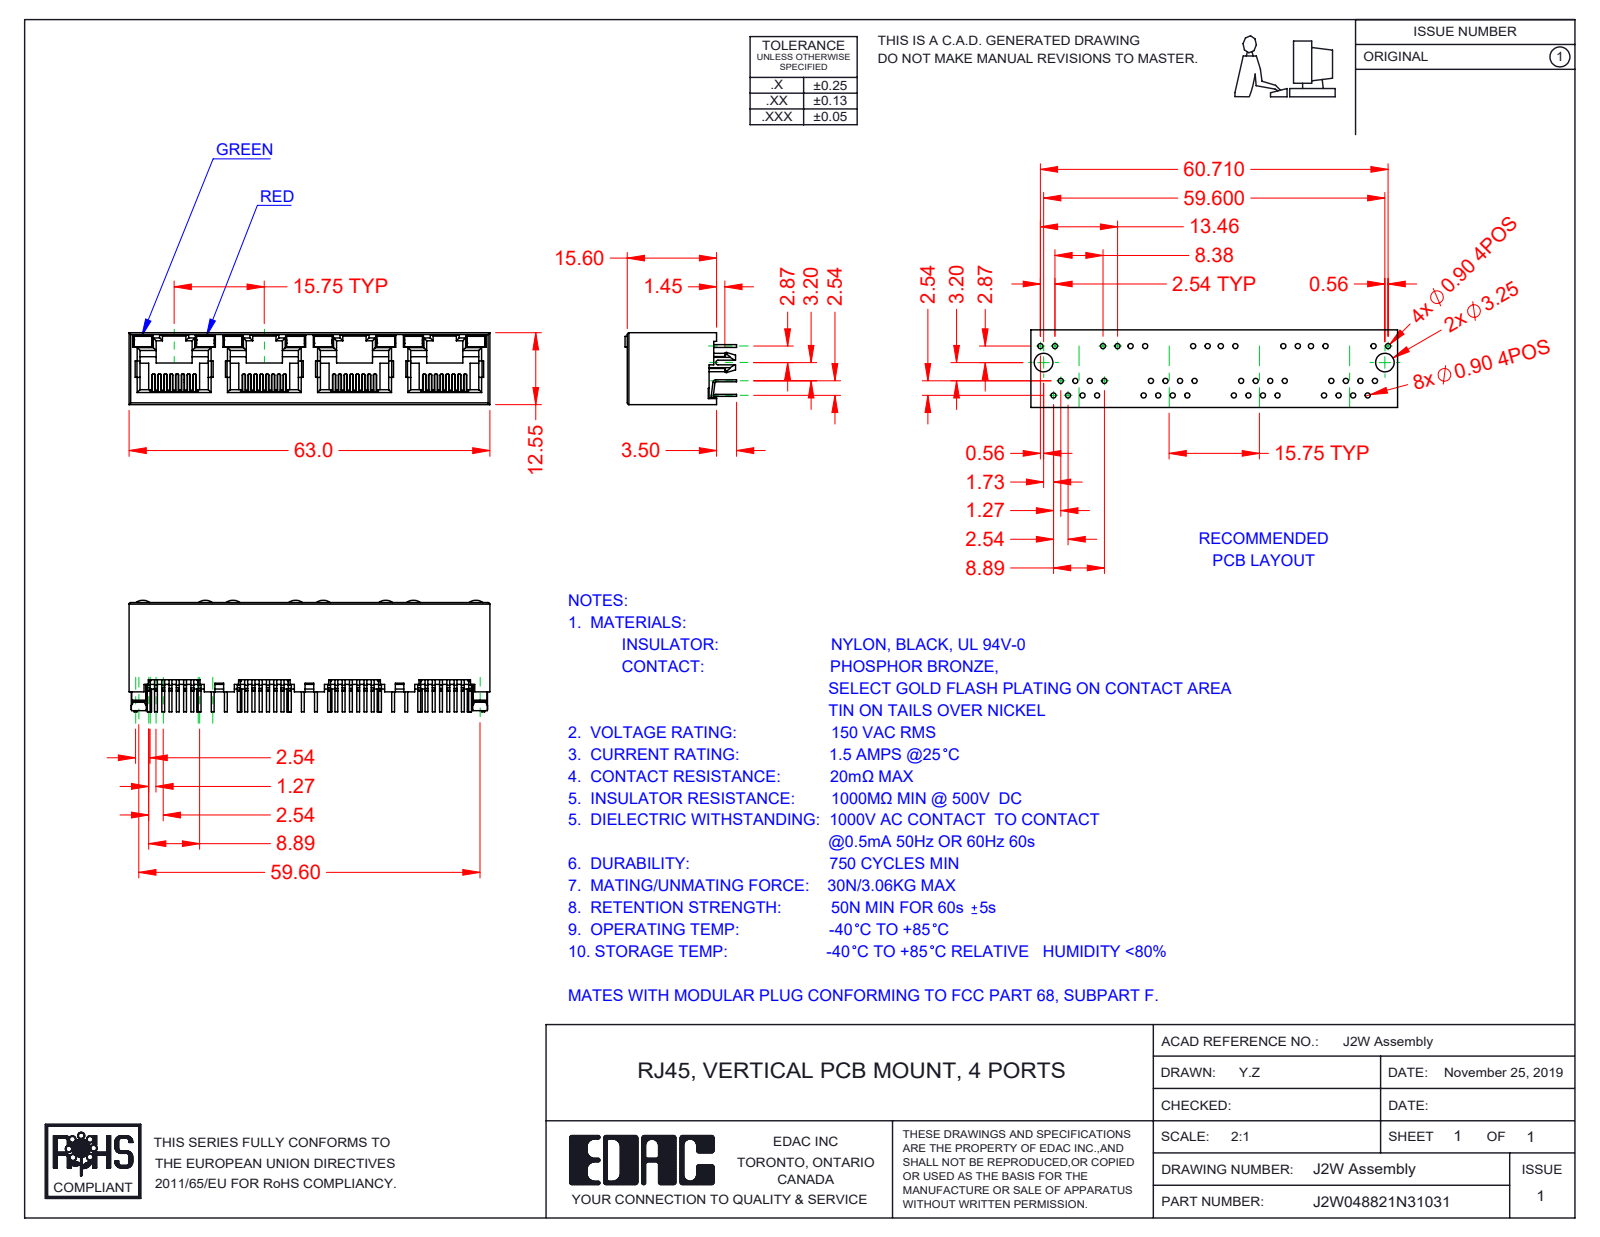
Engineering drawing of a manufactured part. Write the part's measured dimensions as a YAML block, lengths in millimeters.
part_name: "2W LED LH_3-Green; 2W LED RH_2-Red; 2W Insulator; 2W Contact Lock (+2 more)"
step_written_by: "SolidWorks 2016 (CONFIG_CONTROL_DESIGN)"
units: millimeters
bodies: {solids: 45, faces: 3135, planar: 2600, cylindrical: 477, other: 58}
overall_size: [63, 19.5, 12.55]
volume: 5335
surface_area: 13144
partial_cylinders:
  - {radius: 0.15, count: 64}
  - {radius: 0.2, count: 29}
  - {radius: 0.5, count: 28}
  - {radius: 0.3, count: 14}
  - {radius: 0.45, count: 8}
  - {radius: 2, count: 8}
  - {radius: 0.25, count: 2}
  - {radius: 1.5, count: 2}
face_to_face_distances: [12.55, 11.9, 0.65, 15.75, 0.36, 1.5, 0.78, 0.6, 11.3, 31.5]
